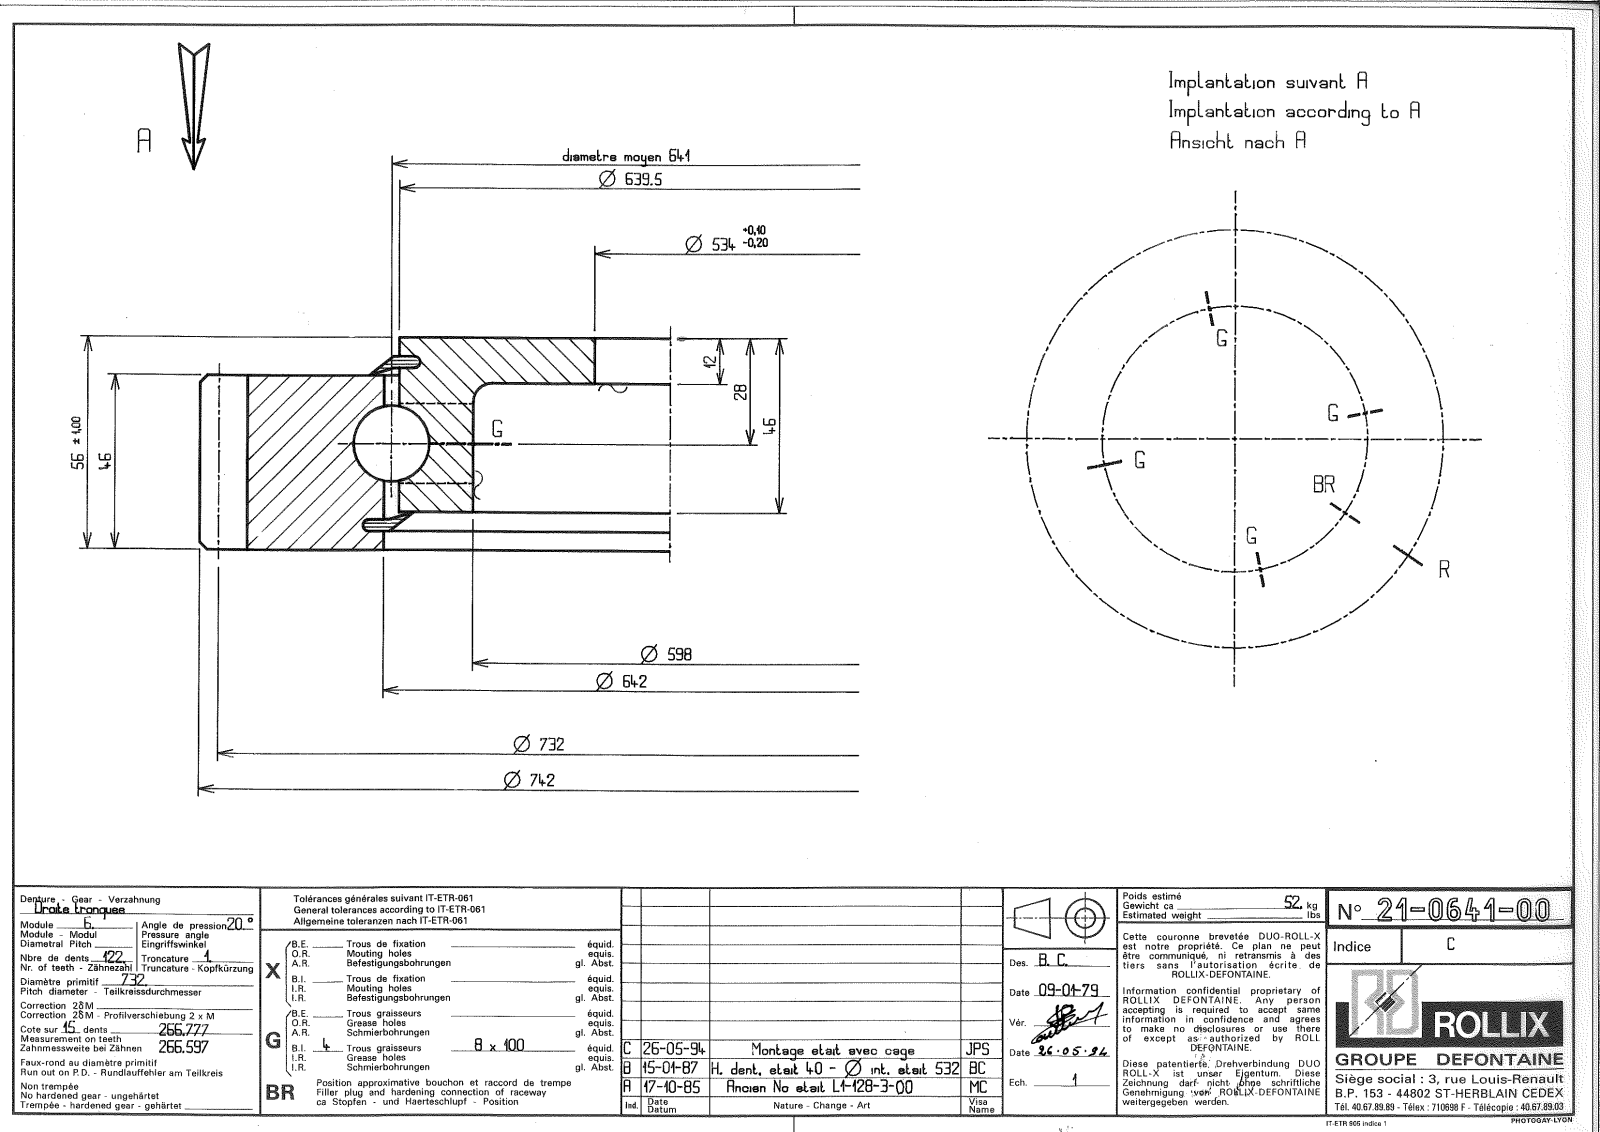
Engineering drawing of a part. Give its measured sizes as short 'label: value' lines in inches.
name: 21-0641-00
written by: SolidWorks 2016 (CONFIG_CONTROL_DESIGN)
unit: in
bodies: 9 solids, 888 faces (297 planar, 277 cylindrical, 314 other)
size: 29.213 × 29.208 × 2.205
volume: 383.7 in³; area: 1 593 in²
holes: 4× ⌀0.276, 1× ⌀21.024, 1× ⌀23.543, 1× ⌀25.413
bosses: 4× ⌀0.315, 1× ⌀25.059
rounds: 1× R14.114, 1× R14.606
face distances: 0.394, 1.811, 2.205, 1.732, 0.079, 0.472, 1.339, 1.417, 0.195, 2.01
hole spacings: 0.018
